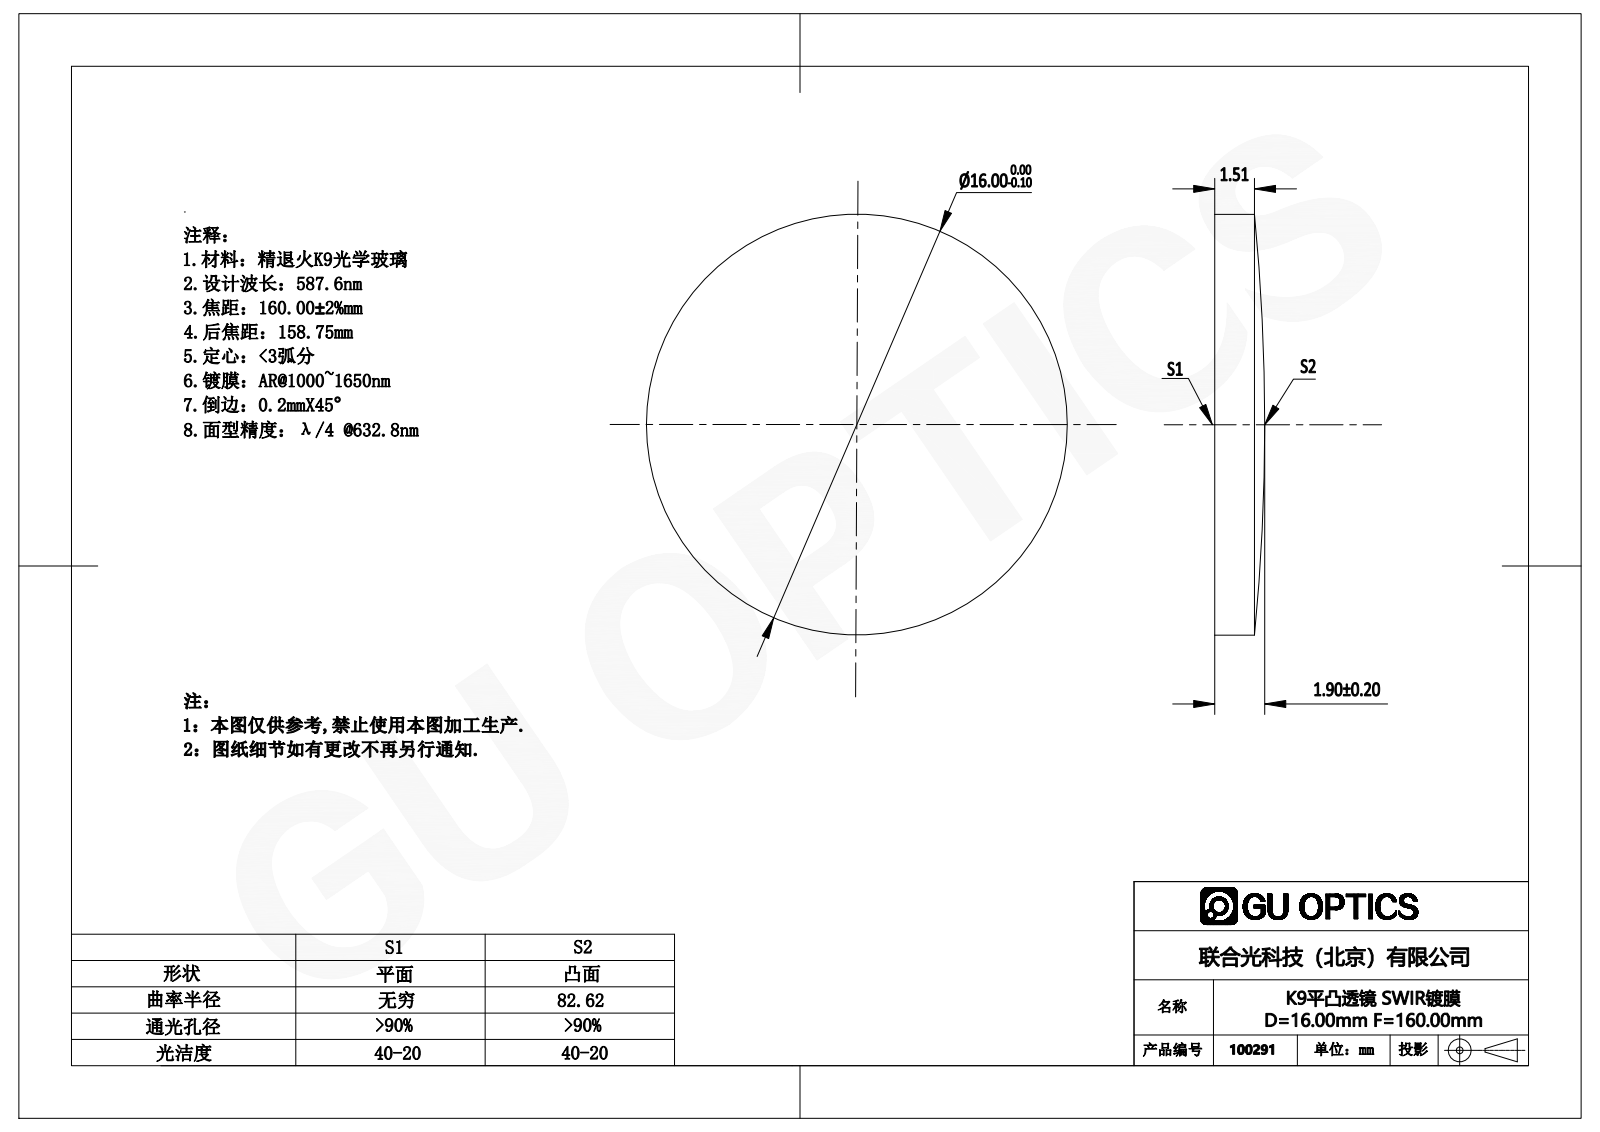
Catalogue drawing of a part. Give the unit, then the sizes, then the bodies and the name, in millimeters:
Units: millimetres
Overall size (bounding box): 16 × 16 × 1.9
Round bosses / shafts (diameter × count): ⌀16 ×1
Volume: 343 mm³ · Surface area: 478 mm²
Bodies: 1 solid, 5 faces (1 planar, 2 cylindrical, 2 other)
Part name (STEP PRODUCT): 100119
STEP written by: SolidWorks 2016 (AUTOMOTIVE_DESIGN)
